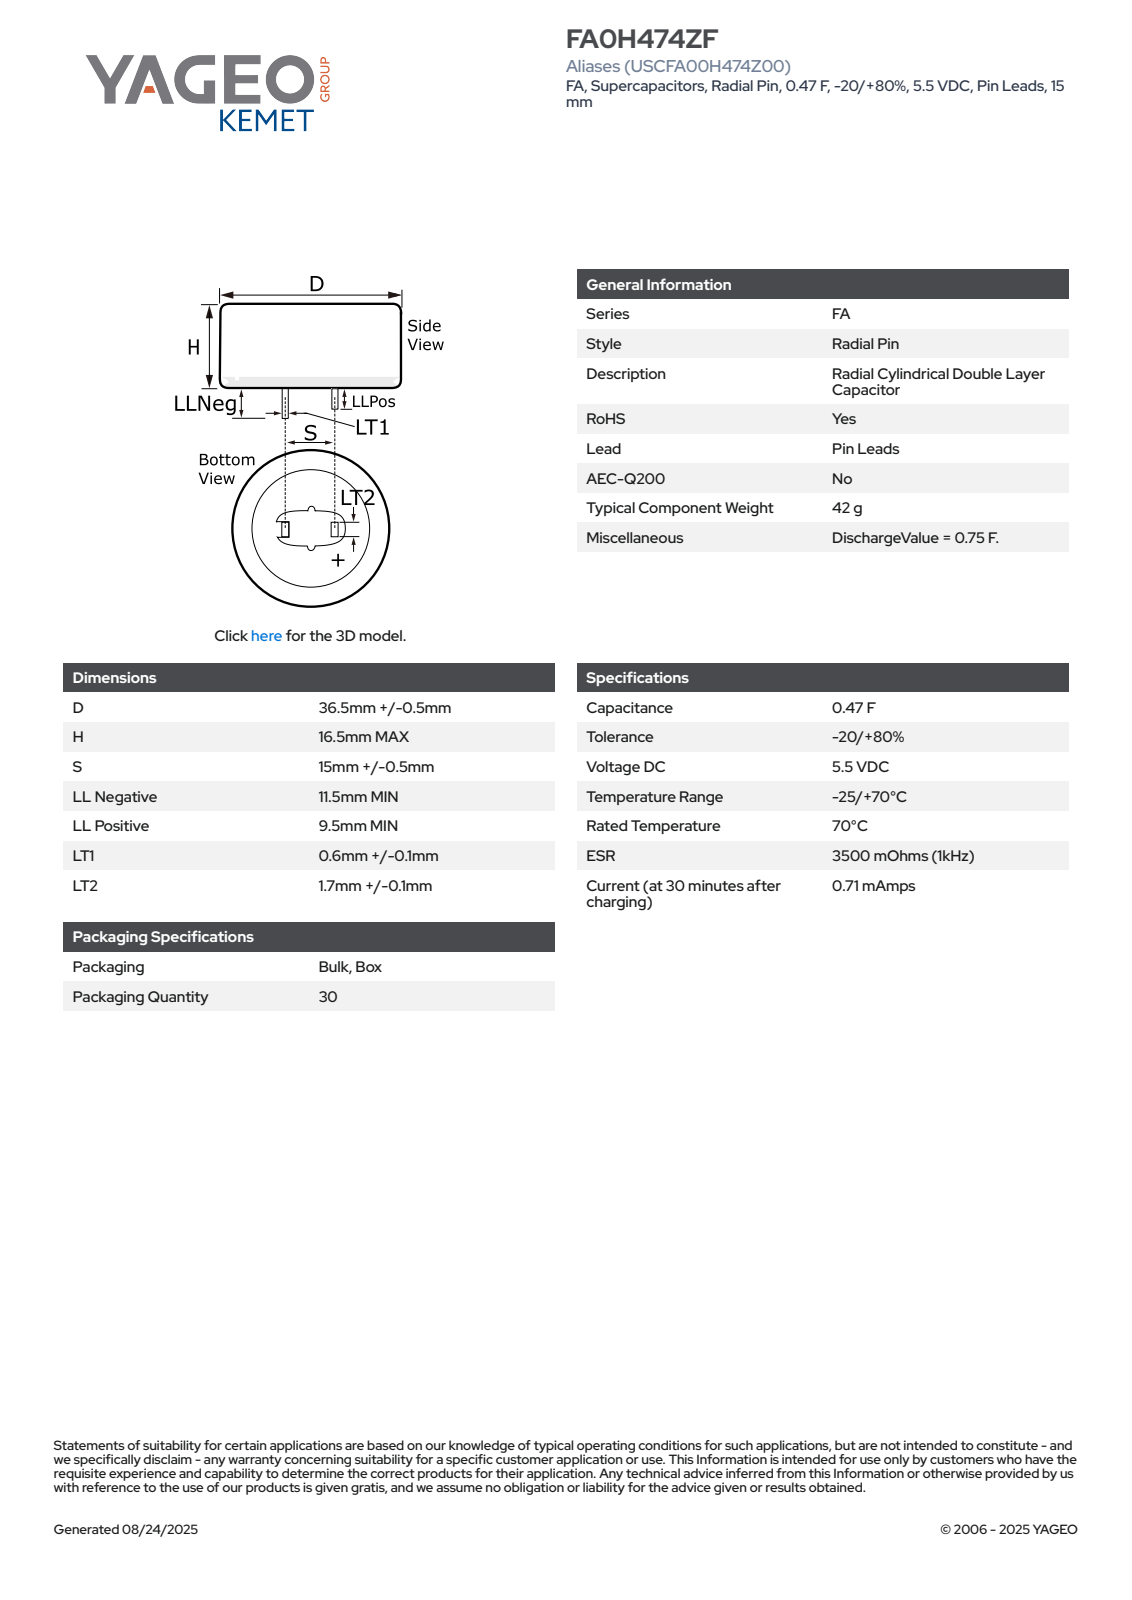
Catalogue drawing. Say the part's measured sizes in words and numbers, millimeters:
The part is named "CDR_LPLLN_D37L16.5S15LLNEG11.5LLPOS9.5LT10.7LT21.8". Its 3-D file was written by "SolidWorks 2014 (AUTOMOTIVE_DESIGN)". It is 1 solid with 78 faces: 70 planar, 4 cylindrical and 4 other. Overall it measures 37 by 37 by 28 millimeters. Its volume is 17 712 cubic millimeters and its surface area 4 067 square millimeters. Round bosses or shafts: 1 of diameter 37. Partial cylindrical surfaces (rounded edges, fillets, slot ends): 1 of radius 18.51. The main face-to-face distances are 16.5, 0.7, 15, 15.7, 14.3, 1.8, 11.5, 28, 2, 9.5.
